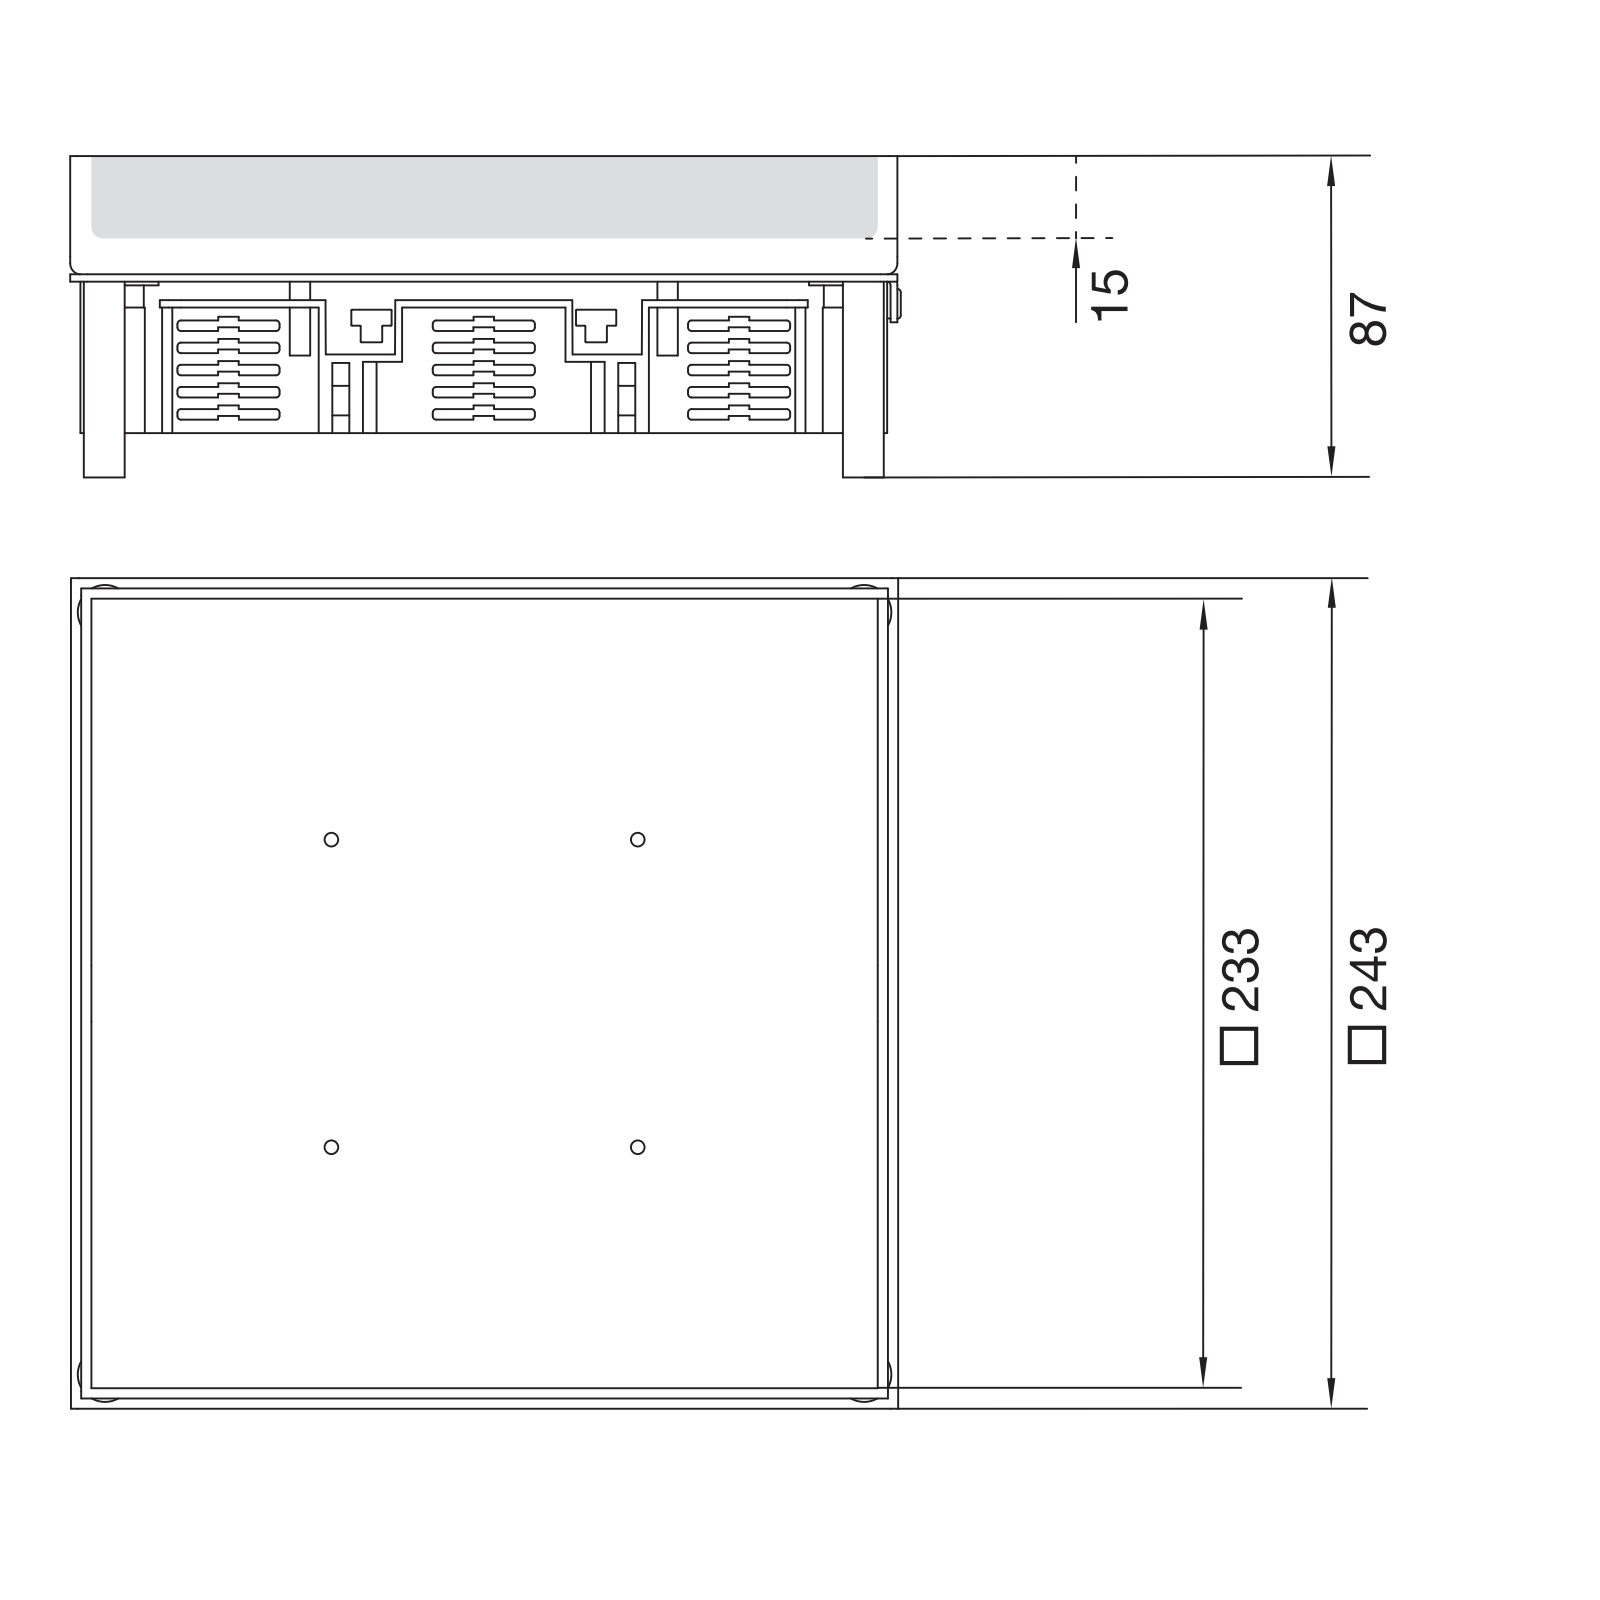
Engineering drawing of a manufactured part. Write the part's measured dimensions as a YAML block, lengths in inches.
part_name: "T-00627; T-00632; T-00625; T-00824_ASM (+4 more)"
step_written_by: "CREO PARAMETRIC BY PTC INC, 2022024 (AUTOMOTIVE_DESIGN)"
units: inches
bodies: {solids: 8, faces: 186, planar: 116, cylindrical: 70, other: 0}
overall_size: [9.567, 9.567, 3.425]
volume: 46.59
surface_area: 640.5
round_holes:
  - {diameter: 0.197, count: 4}
  - {diameter: 0.268, count: 4}
  - {diameter: 0.335, count: 4}
  - {diameter: 4.606, count: 1}
round_bosses_or_shafts:
  - {diameter: 0.472, count: 4}
  - {diameter: 0.388, count: 4}
partial_cylinders:
  - {radius: 0.039, count: 8}
  - {radius: 0.118, count: 8}
  - {radius: 0.079, count: 4}
  - {radius: 5.906, count: 1}
  - {radius: 6.004, count: 1}
face_to_face_distances: [0.079, 0.118, 0.472, 0.394, 0.098, 9.252, 0.197, 9.232, 0.138, 0.236]
hole_center_spacings: [6.694, 2.506, 3.543, 3.703, 6.208, 8.713, 8.78, 5.011]
